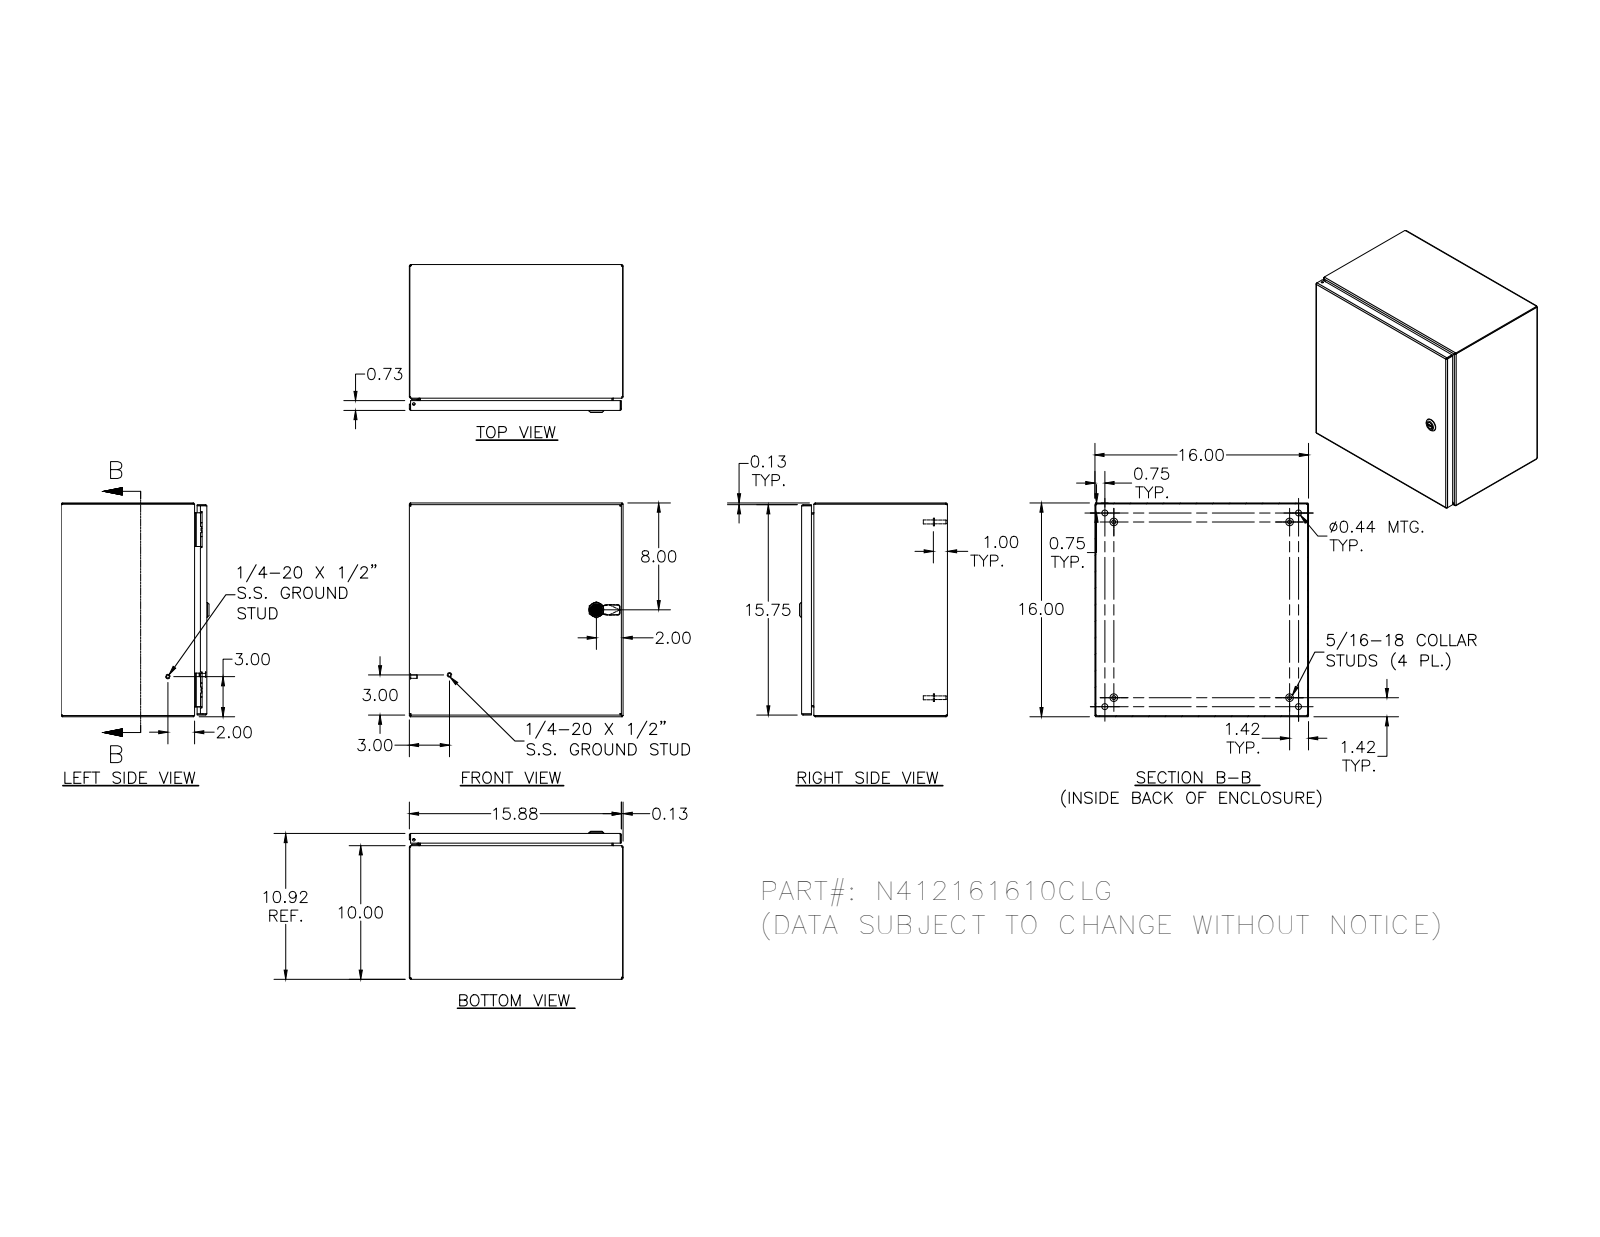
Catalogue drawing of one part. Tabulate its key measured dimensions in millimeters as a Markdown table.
| quantity | value |
| --- | --- |
| part name | N412161610CLG |
| STEP written by | SolidWorks 2018 (AUTOMOTIVE_DESIGN) |
| units | millimeters |
| bodies | 33 solids, 1449 faces (530 planar, 547 cylindrical, 372 other) |
| overall size | 406.4 × 406.4 × 281.3 |
| volume | 1 559 000 mm³ |
| surface area | 1 670 000 mm² |
| round holes (diameter × count) | 4.8 × 5, 2.4 × 4, 3.9 × 4, 4.2 × 4, 4.4 × 4, 11.1 × 4, 4 × 2, 4.7 × 1, 5 × 1, 8 × 1, 10 × 1, 10.2 × 1 |
| round bosses / shafts (diameter × count) | 6.4 × 10, 3.3 × 5, 14.3 × 4, 9.1 × 4, 8.1 × 4, 7.6 × 4, 7 × 4, 6.5 × 4 |
| partial cylindrical surfaces (radius × count) | 0.3 × 30, 0.8 × 30, 1.3 × 26, 2.7 × 20, 0.4 × 18, 3.2 × 16, 0.5 × 13, 0.8 × 8 |
| main face-to-face distances | 1.9, 275.4, 404.5, 402.6, 1.9, 404.5, 406.4, 273.5, 277.3, 23.3 |
| hole center spacings | 304.8, 16.8, 16.7, 33.2, 49.9, 288, 304.7, 321.5 |
